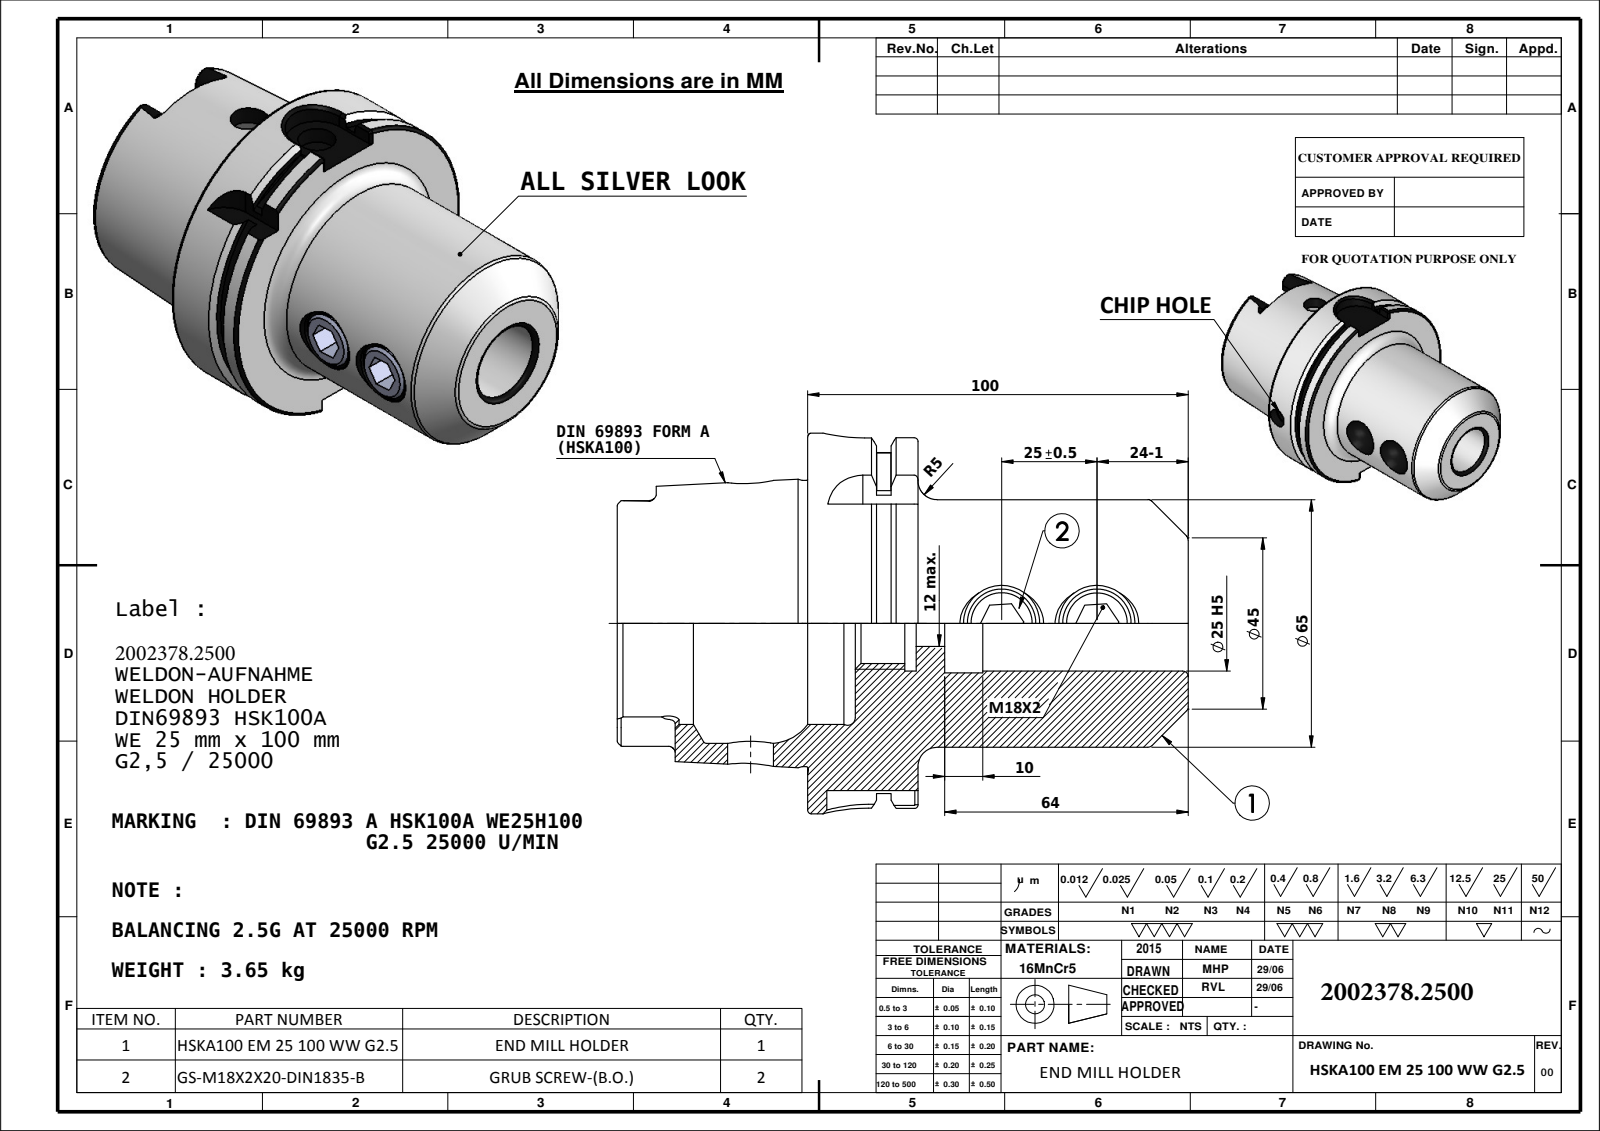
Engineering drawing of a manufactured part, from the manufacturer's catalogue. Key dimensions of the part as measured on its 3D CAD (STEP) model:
Part name (STEP PRODUCT): HSKA100 EM 25 100 WW G2.5; 91100A-WE8 25100; GS-M18X2X20
STEP written by: SolidWorks 2009 (CONFIG_CONTROL_DESIGN)
Units: millimetres
Bodies: 3 solids, 230 faces (74 planar, 64 cylindrical, 92 other)
Overall size (bounding box): 150 × 100 × 100
Volume: 445 012 mm³ · Surface area: 73 091 mm²
Round holes (diameter × count): ⌀12 ×3, ⌀16 ×2, ⌀20 ×2, ⌀10 ×1, ⌀21 ×1, ⌀25 ×1, ⌀26 ×1, ⌀53 ×1, ⌀63 ×1
Round bosses / shafts (diameter × count): ⌀18 ×2, ⌀100 ×1, ⌀92 ×1, ⌀75.16 ×1, ⌀65 ×1
Partial cylindrical surfaces — rounded edges, fillets, slot ends (radius × count): R1.8 ×6, R4.88 ×4, R10 ×2, R11 ×1
Main face-to-face distances: 29, 12.5, 16.5, 50, 62.5, 79, 150, 100, 87.5, 71
Hole centre spacings: 25, 30, 44, 69
